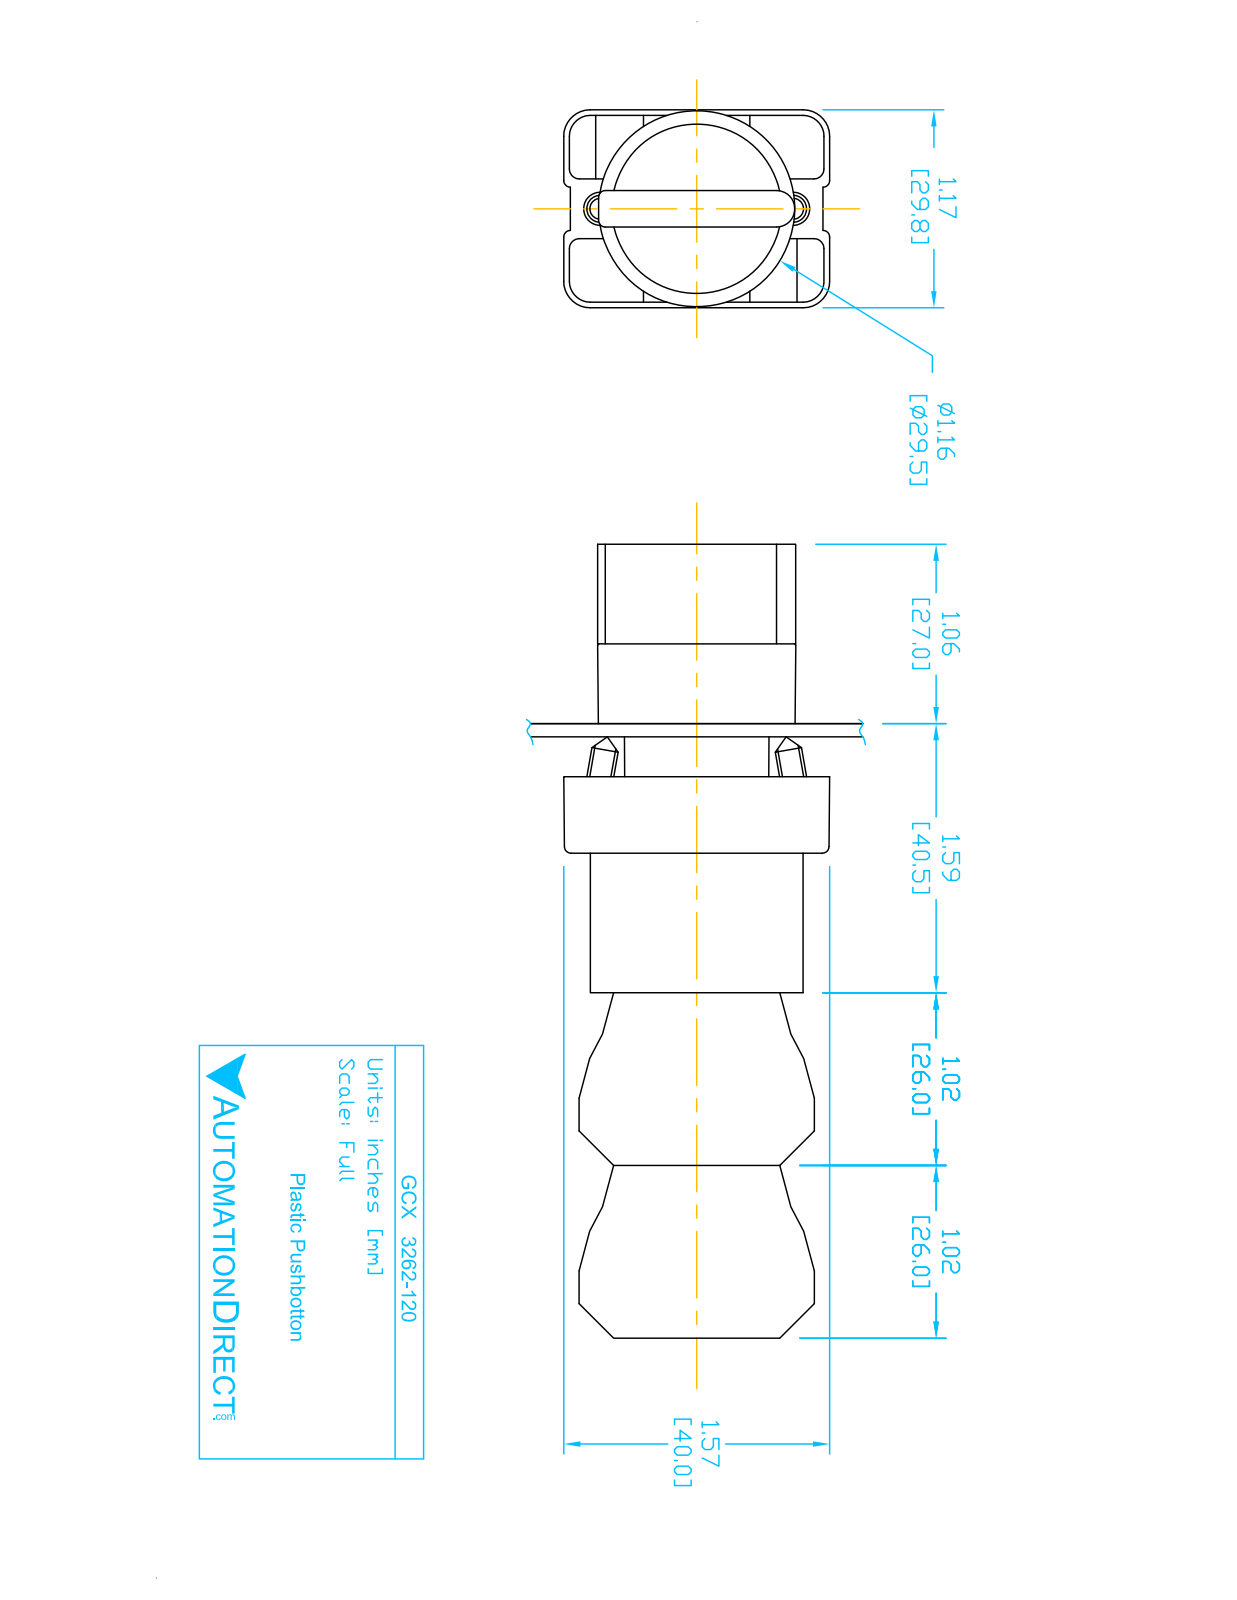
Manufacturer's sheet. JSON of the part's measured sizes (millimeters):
{"part_name": "GCX3262 OPERATOR; ECX1050; ECX3029-2; GCX3262-120 (+2 more)", "step_written_by": "SolidWorks 2016 (AUTOMOTIVE_DESIGN)", "units": "millimeters", "bodies": {"solids": 11, "faces": 724, "planar": 488, "cylindrical": 193, "other": 43}, "overall_size": [118.8, 40.2, 29.9], "volume_mm3": 77850, "surface_area_mm2": 38210, "round_holes": [[2, 4], [2.2, 2], [3.1, 2], [3.3, 2], [5, 1], [11.9, 1], [22.3, 1], [22.6, 1], [26, 1]], "round_bosses_or_shafts": [[4, 4], [29.8, 1], [25.5, 1], [24, 1], [21.7, 1], [19.8, 1], [12.8, 1]], "partial_cylinders_radius": [[1.5, 24], [1, 12], [3.1, 12], [4, 12], [1, 9], [0.5, 2], [1.6, 2], [2, 2]], "face_to_face_distances": [14.7, 15.1, 26, 29.7, 0.4, 21, 47, 77.3, 51.3, 30.3], "hole_center_spacings": [6, 25.5, 24.7, 12, 13.7, 13.8, 27.5, 12.3]}
